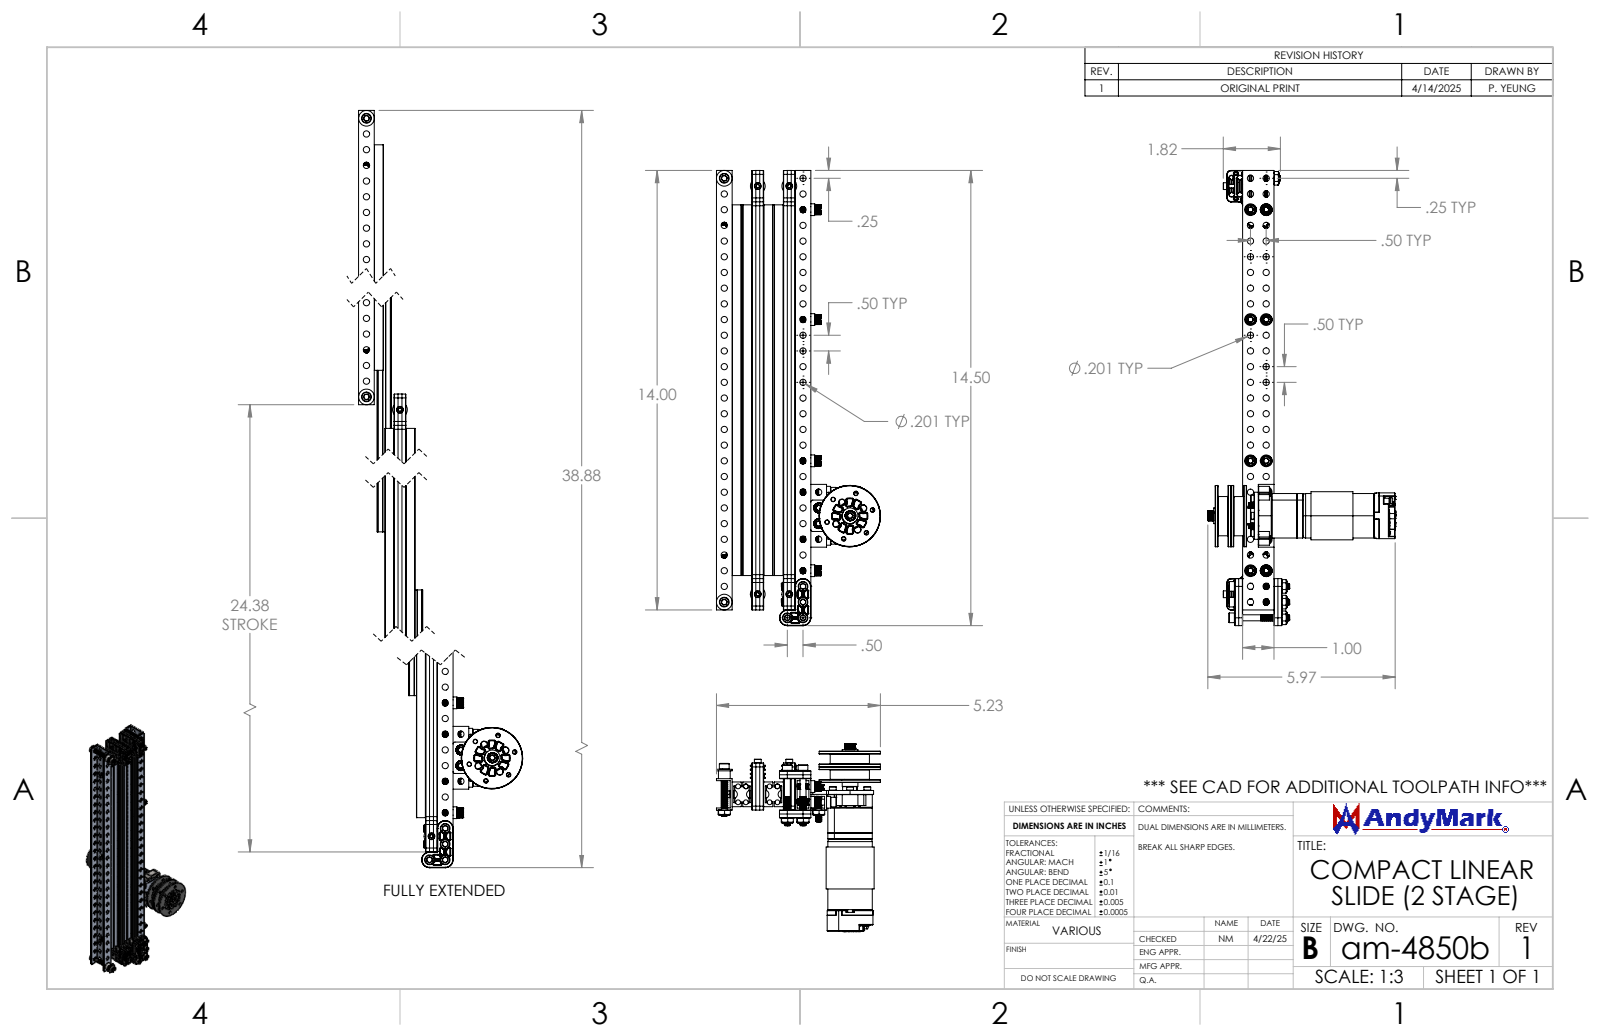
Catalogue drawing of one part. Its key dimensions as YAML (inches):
part_name: "NeveRest Hex Shaft 375H 1IN Long; am-5004_2x3 RoBits 2x3 L Gusset; am-5001-0200 RoBits 0.5x0.5x2.0 Tube; am-5009-1400 Robits 1.0x0.5x14.0 Channel (+8 more)"
step_written_by: "SolidWorks 2024 (AUTOMOTIVE_DESIGN)"
units: inches
bodies: {solids: 248, faces: 39023, planar: 7009, cylindrical: 12719, other: 19295}
overall_size: [14.5, 5.985, 5.227]
volume: 27.01
surface_area: 668.3
round_holes:
  - {diameter: 0.201, count: 122}
  - {diameter: 0.164, count: 80}
  - {diameter: 0.161, count: 20}
  - {diameter: 0.239, count: 20}
  - {diameter: 0.125, count: 15}
  - {diameter: 0.194, count: 11}
  - {diameter: 0.098, count: 10}
  - {diameter: 0.024, count: 9}
  - {diameter: 0.125, count: 9}
  - {diameter: 0.126, count: 6}
  - {diameter: 0.118, count: 5}
  - {diameter: 0.159, count: 5}
round_bosses_or_shafts:
  - {diameter: 0.19, count: 21}
  - {diameter: 0.375, count: 13}
  - {diameter: 0.118, count: 13}
  - {diameter: 0.217, count: 12}
  - {diameter: 0.313, count: 11}
  - {diameter: 0.312, count: 10}
  - {diameter: 0.093, count: 10}
  - {diameter: 0.028, count: 6}
partial_cylinders:
  - {radius: 0.01, count: 2752}
  - {radius: 0.008, count: 137}
  - {radius: 0.004, count: 92}
  - {radius: 0.005, count: 75}
  - {radius: 0.012, count: 74}
  - {radius: 0.02, count: 59}
  - {radius: 0.031, count: 32}
  - {radius: 0.02, count: 24}
face_to_face_distances: [1.005, 0.063, 0.5, 0.437, 0.63, 0.894, 0.106, 0.375, 0.055, 0.575]
hole_center_spacings: [0.5, 1, 1.5, 2, 2.5, 3, 3.5, 4]
